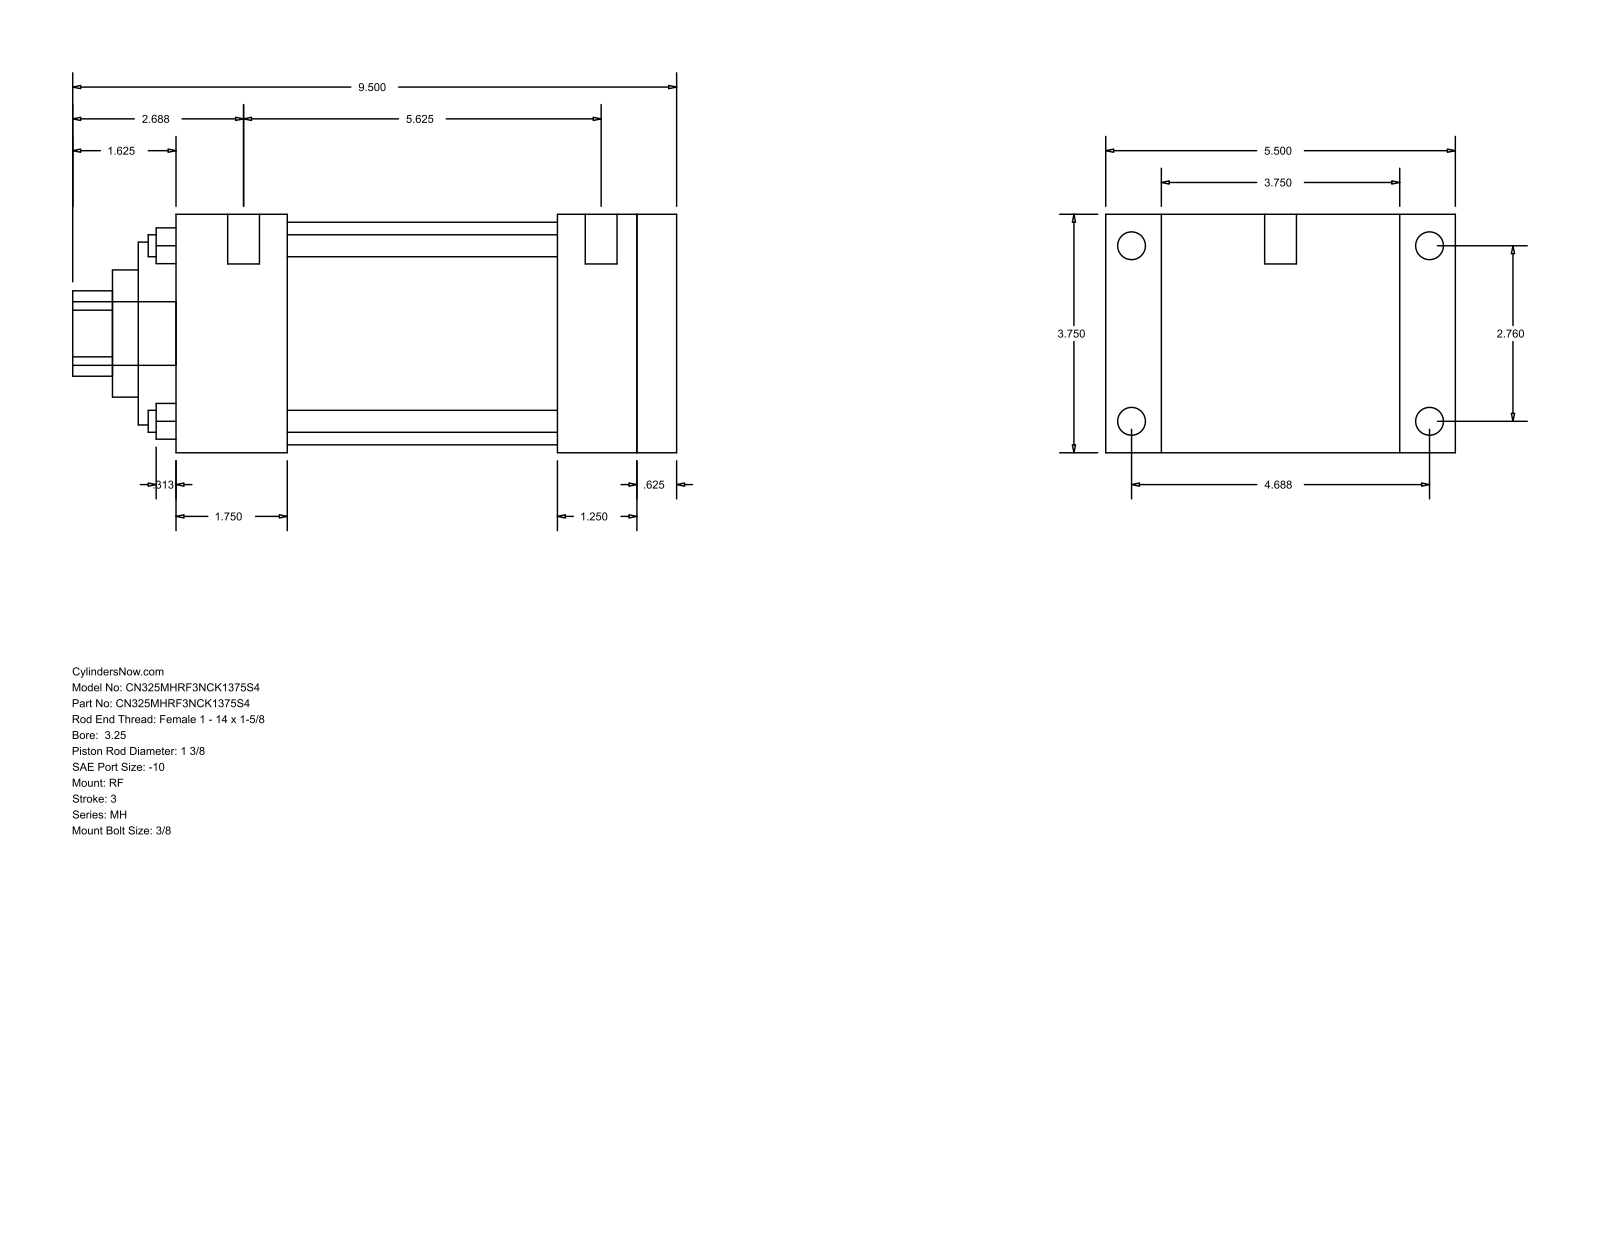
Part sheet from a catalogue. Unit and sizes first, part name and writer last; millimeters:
Units: millimetres
Overall size (bounding box): 241.3 × 139.7 × 95.25
Round holes (diameter × count): ⌀8.76 ×4, ⌀34.92 ×1, ⌀50.8 ×1, ⌀73.03 ×1, ⌀88.9 ×1
Round bosses / shafts (diameter × count): ⌀11.13 ×4, ⌀5.56 ×4, ⌀12.7 ×2, ⌀25.4 ×1
Partial cylindrical surfaces — rounded edges, fillets, slot ends (radius × count): R17.06 ×1
Main face-to-face distances: 95.24, 200.03, 184.16, 15.87, 22.23, 117.47, 44.45, 139.71, 155.58, 152.41
Hole centre spacings: 49.57, 70.1, 99.14
Bodies: 0 solids, 94 faces (65 planar, 29 cylindrical, 0 other)
Part name (STEP PRODUCT): MH_RF__0325_1.375
STEP written by: GSSL Pune (CONFIG_CONTROL_DESIGN)
